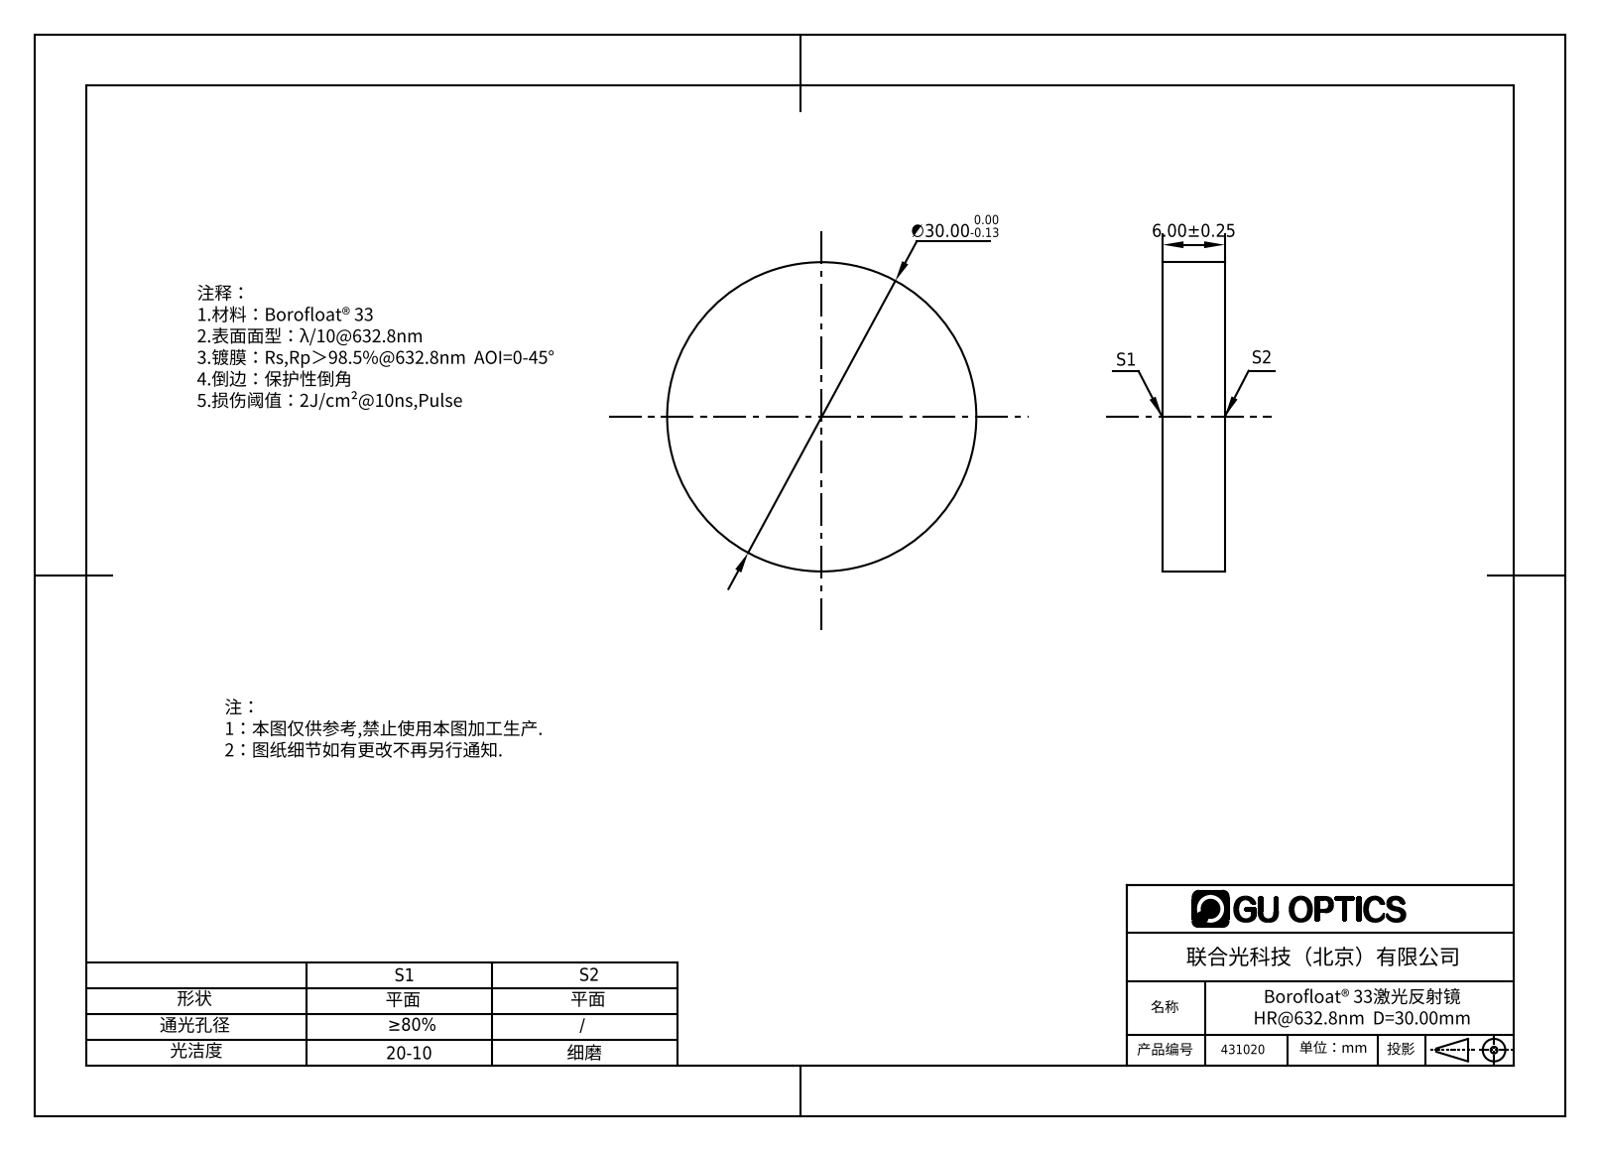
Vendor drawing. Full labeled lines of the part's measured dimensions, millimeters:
Part name (STEP PRODUCT): 431020
STEP written by: SolidWorks 2016 (AUTOMOTIVE_DESIGN)
Units: millimetres
Bodies: 1 solid, 4 faces (2 planar, 2 cylindrical, 0 other)
Overall size (bounding box): 30 × 30 × 6
Volume: 4 241 mm³ · Surface area: 1 979 mm²
Round bosses / shafts (diameter × count): ⌀30 ×1
Main face-to-face distances: 6
